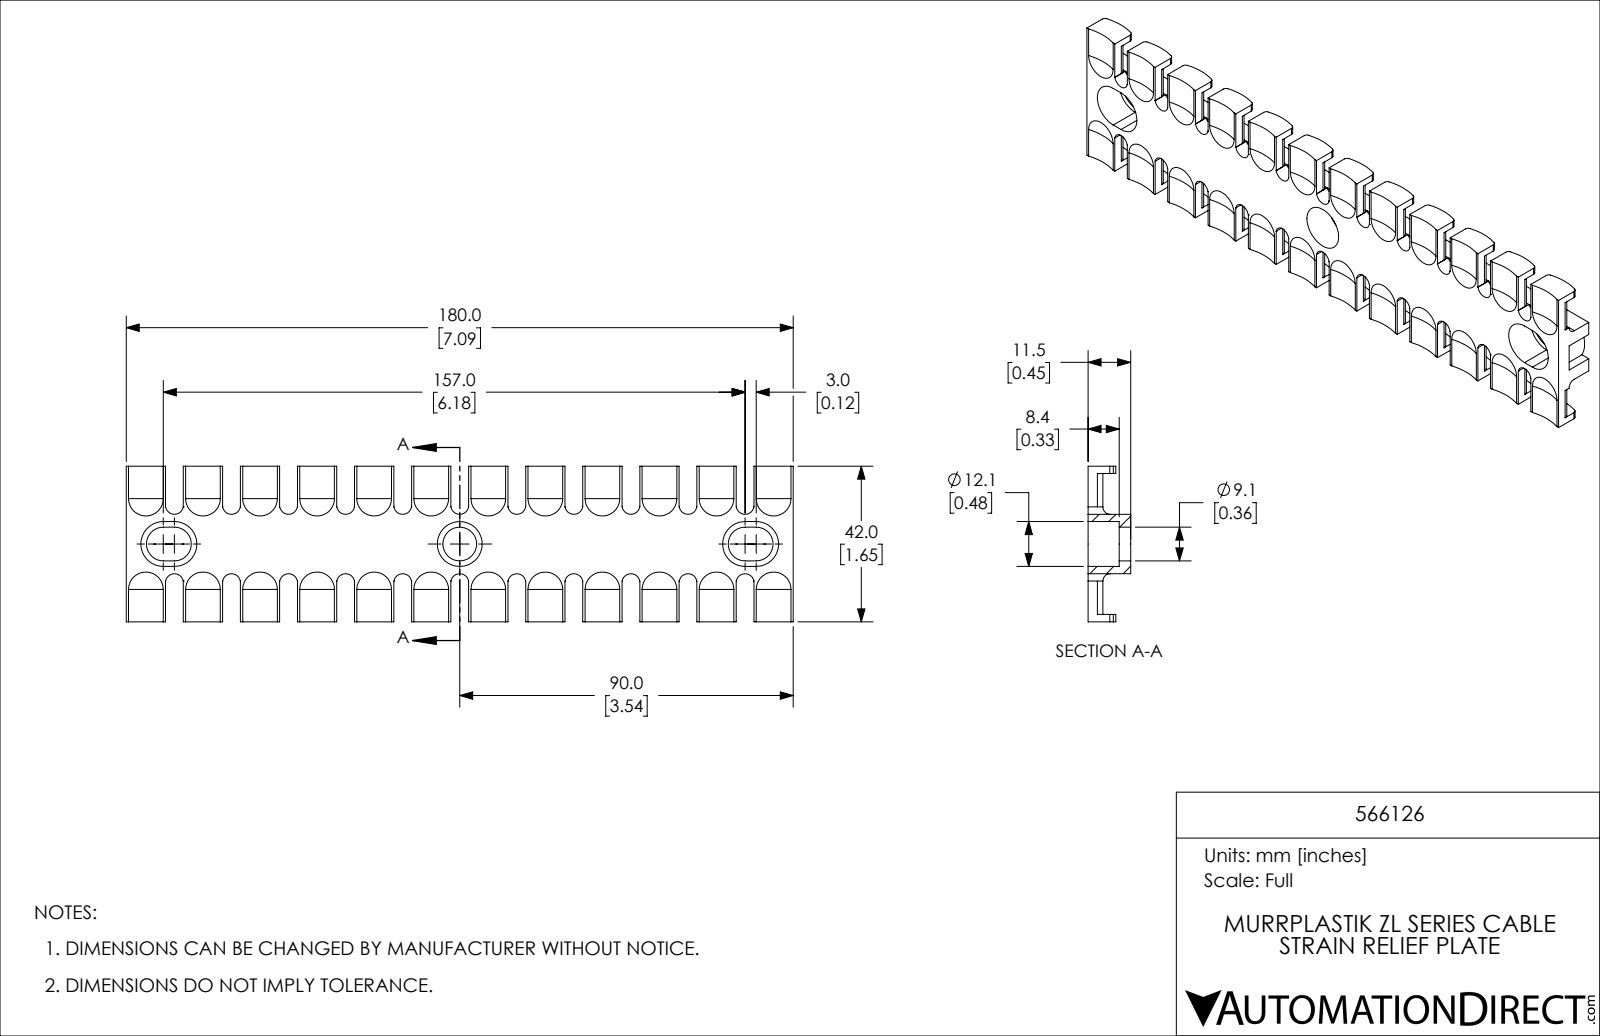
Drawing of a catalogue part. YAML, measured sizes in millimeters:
part_name: "566126"
step_written_by: "SolidWorks 2019 (CONFIG_CONTROL_DESIGN)"
units: millimeters
bodies: {solids: 1, faces: 478, planar: 203, cylindrical: 251, other: 24}
overall_size: [180, 42, 11.5]
volume: 35467
surface_area: 23881
round_holes:
  - {diameter: 9.1, count: 1}
  - {diameter: 12.1, count: 1}
partial_cylinders:
  - {radius: 1, count: 24}
  - {radius: 1.5, count: 24}
  - {radius: 16, count: 24}
  - {radius: 2.4, count: 22}
  - {radius: 4.55, count: 4}
  - {radius: 6.05, count: 4}
  - {radius: 2, count: 2}
  - {radius: 8.4, count: 2}
face_to_face_distances: [4, 12, 29, 13, 17, 25, 7.5, 11.5, 15.4, 30.8]
